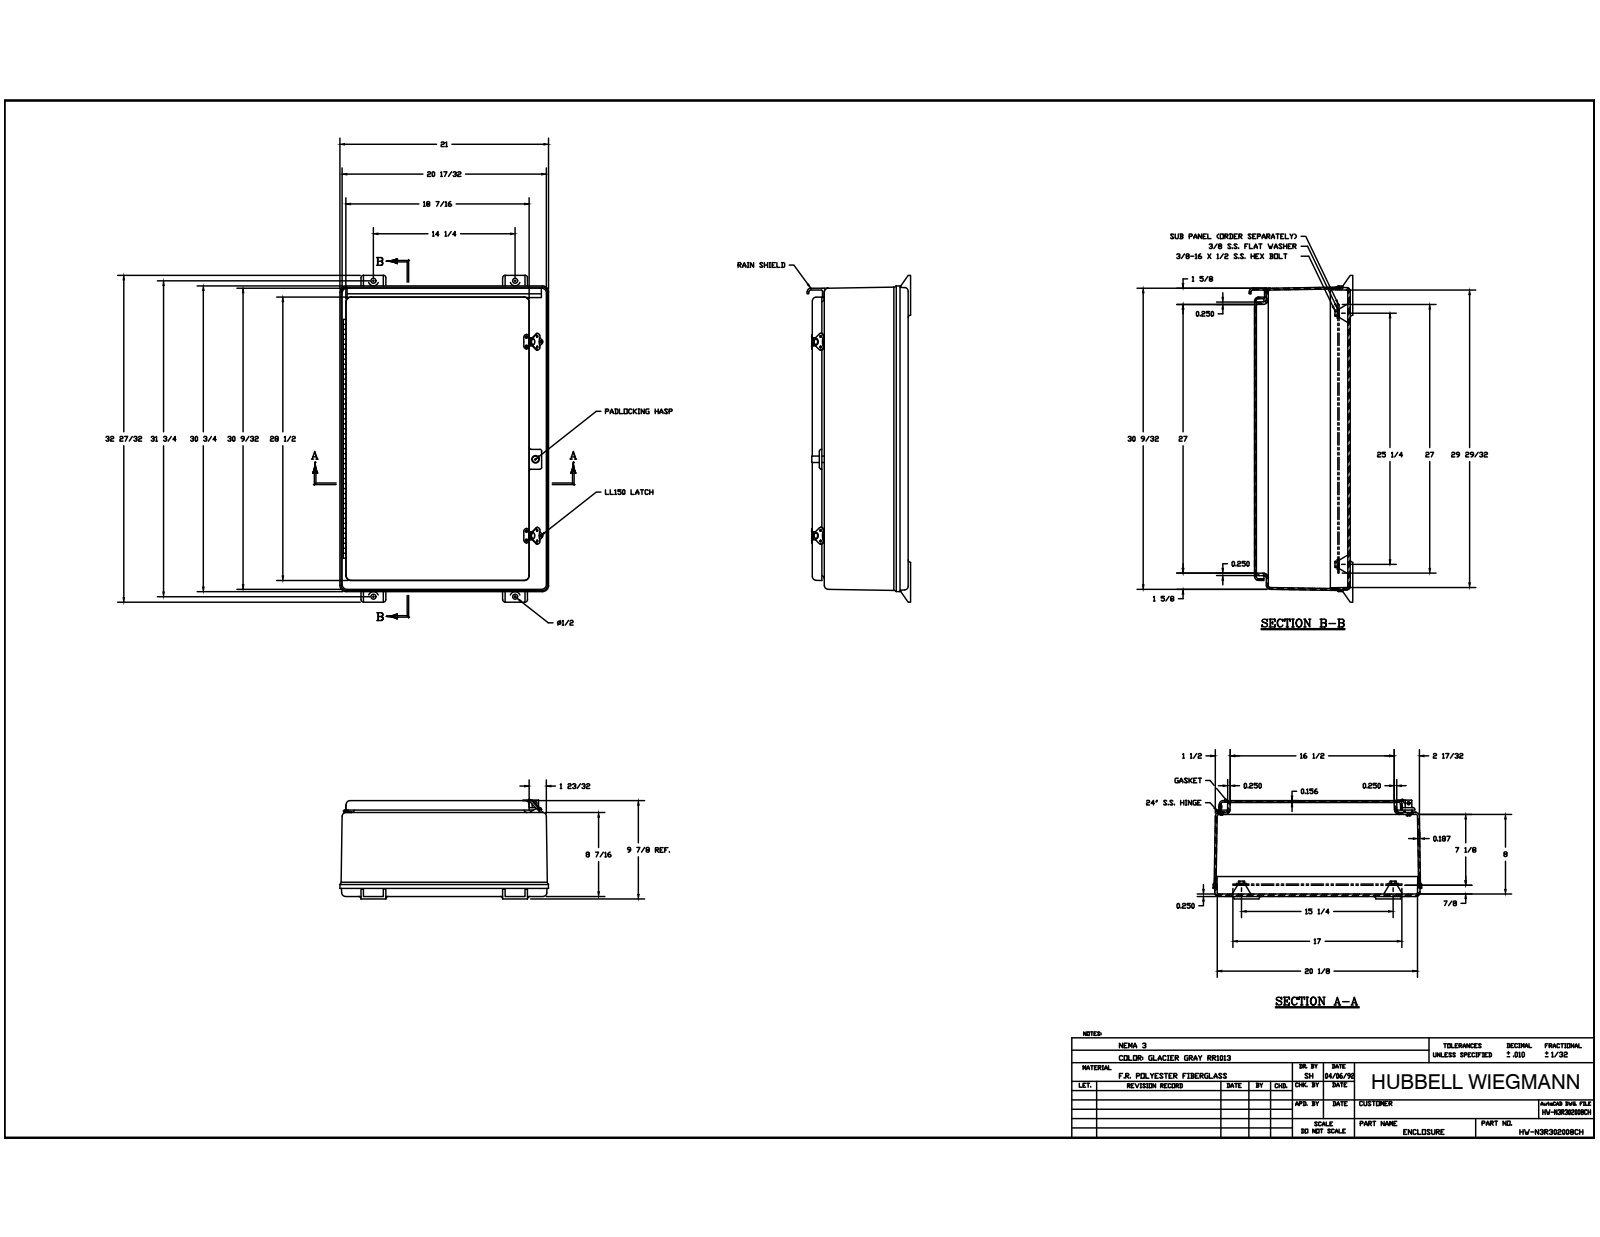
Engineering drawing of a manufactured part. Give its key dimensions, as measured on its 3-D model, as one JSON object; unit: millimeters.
{"part_name": "WPN30208SRT; WPN3020B; N3020RS; LL150 LATCH KEEPER PAD (+8 more)", "step_written_by": "Autodesk Inventor 2014 (AUTOMOTIVE_DESIGN)", "units": "millimeters", "bodies": {"solids": 40, "faces": 1210, "planar": 486, "cylindrical": 476, "other": 248}, "overall_size": [834.23, 533.4, 265.1], "volume_mm3": 8052000, "surface_area_mm2": 3357000, "round_holes": [[3.3, 25], [1.65, 11], [1.59, 8], [3.5, 4], [4.76, 4], [14.3, 4], [12.95, 2], [12.96, 2], [3.17, 1], [3.43, 1], [3.97, 1], [5.11, 1]], "round_bosses_or_shafts": [[7.54, 11], [3.56, 8], [12.7, 2], [6.35, 1], [5.11, 1], [5.08, 1]], "partial_cylinders_radius": [[0.25, 60], [6.35, 24], [4.76, 22], [9.53, 16], [12.7, 12], [7.94, 10], [0.76, 8], [3.17, 7]], "face_to_face_distances": [4.75, 6.35, 3.97, 244.48, 238.13, 240.51, 234.16, 214.3, 207.95, 26.21], "hole_center_spacings": [495.3, 23.82, 39.16, 190.5, 393.7, 21.79, 21.8, 63.14]}
